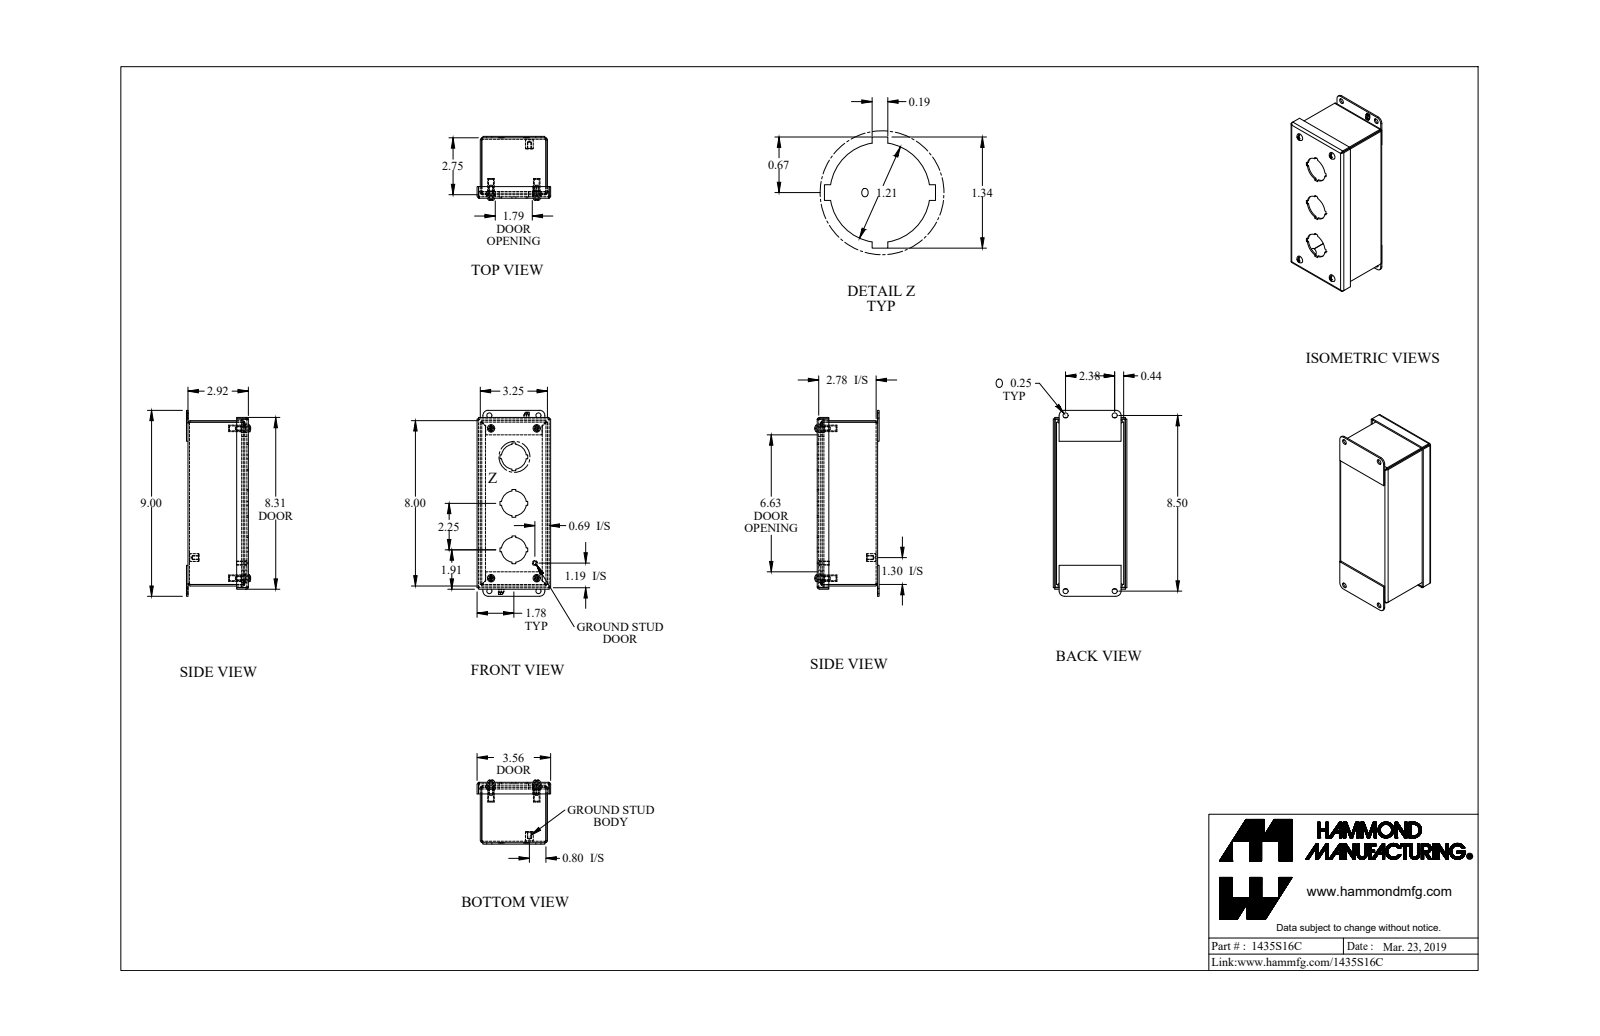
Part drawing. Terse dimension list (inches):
name: 1435S16C_Default
written by: SolidWorks 2019 (CONFIG_CONTROL_DESIGN)
unit: in
bodies: 19 solids, 493 faces (319 planar, 144 cylindrical, 30 other)
size: 9 × 3.562 × 3.104
volume: 12.11 in³; area: 317.5 in²
holes: 8× ⌀0.25, 4× ⌀0.065, 4× ⌀0.239, 4× ⌀0.253, 4× ⌀0.406, 3× ⌀1.21, 1× ⌀0.156
bosses: 5× ⌀0.19, 4× ⌀0.406, 4× ⌀0.315, 4× ⌀0.148, 1× ⌀0.375, 1× ⌀0.25
rounds: 12× R0.036, 12× R0.108, 4× R0.171, 4× R0.25, 1× R0.125
face distances: 0.072, 2.85, 0.072, 3.178, 2.922, 2.778, 3.106, 3.25, 7.928, 0.156
hole spacings: 7.25, 2.211, 7.58, 7.876, 2.212, 0.63, 0.63, 2.377
